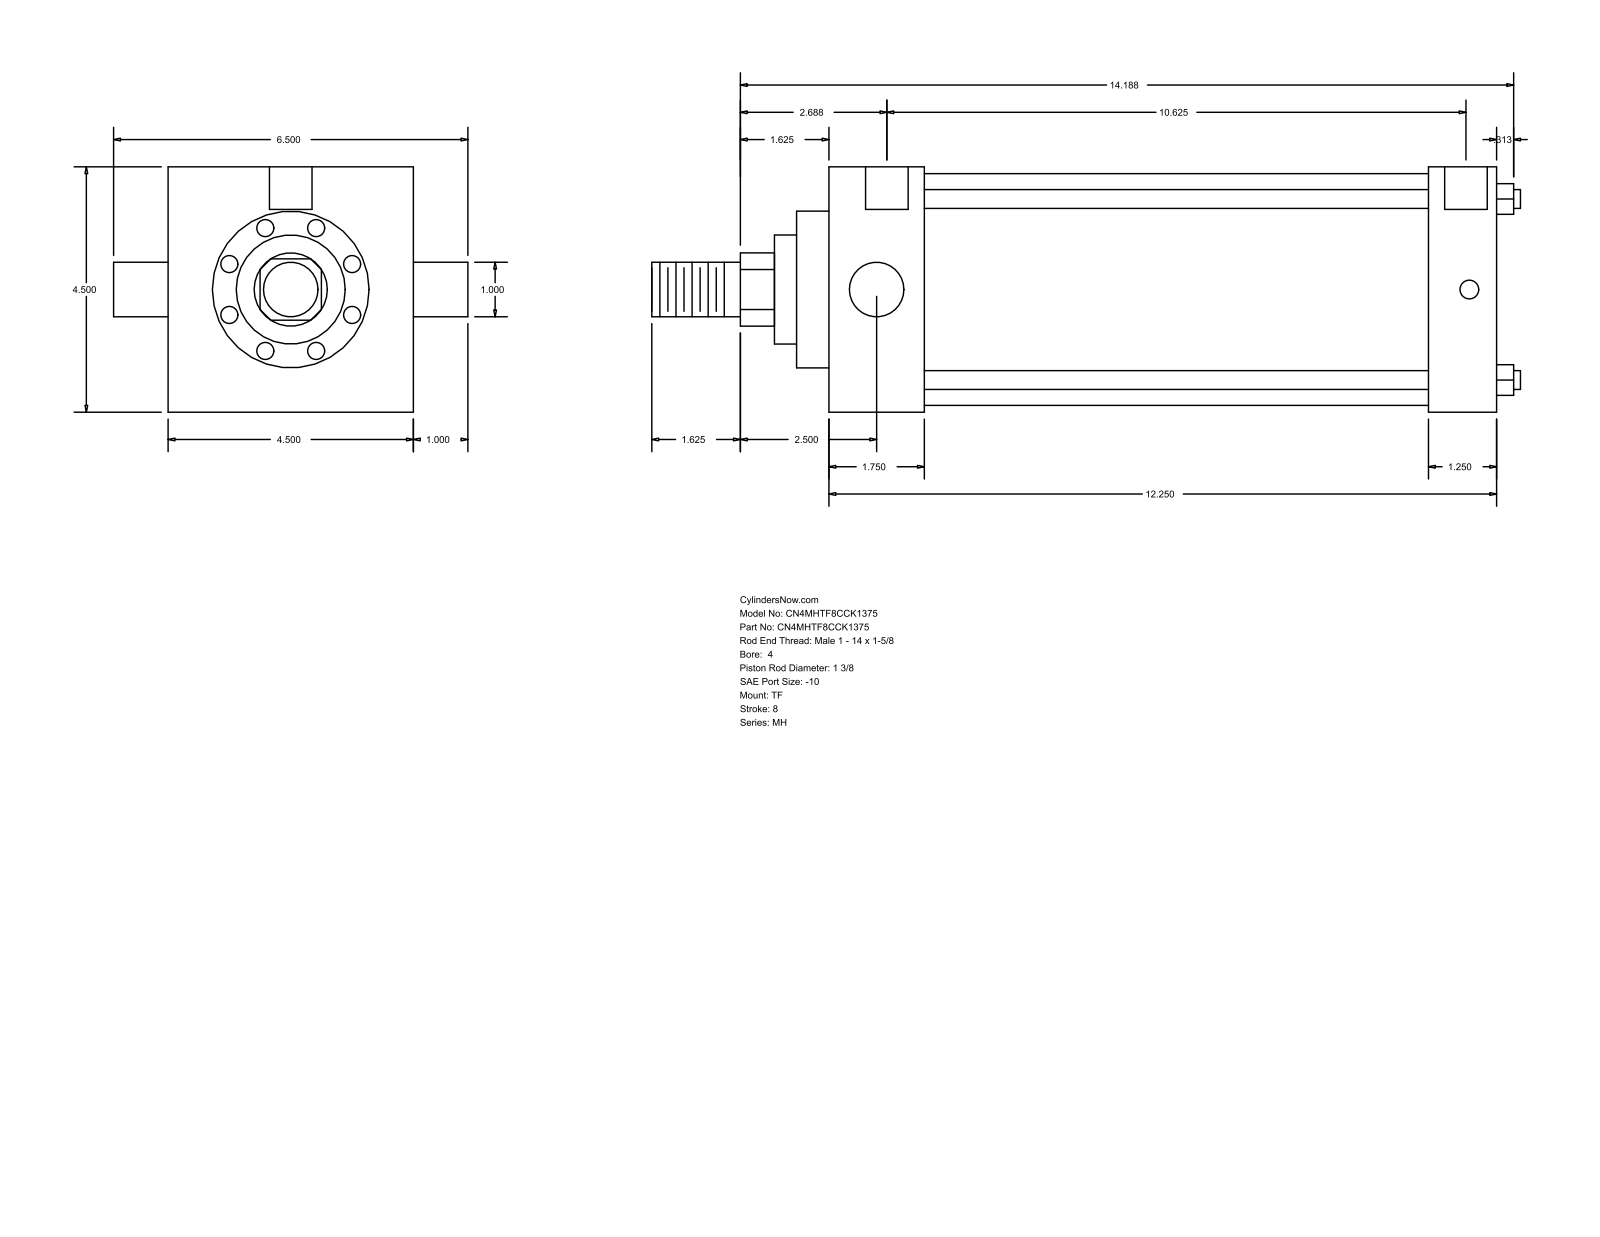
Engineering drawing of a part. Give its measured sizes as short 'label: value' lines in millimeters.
name: MH_TF__0400_1.375
written by: GSSL Pune (CONFIG_CONTROL_DESIGN)
unit: mm
bodies: 0 solids, 86 faces (61 planar, 25 cylindrical, 0 other)
size: 404.81 × 165.1 × 114.3
holes: 3× ⌀8.73, 2× ⌀19.84
bosses: 4× ⌀8.76, 2× ⌀25.4, 1× ⌀107.95, 1× ⌀73.03, 1× ⌀50.8, 1× ⌀34.92
rounds: 1× R17.06
face distances: 114.3, 311.16, 44.45, 266.71, 279.41, 234.96, 31.75, 15.08, 59.53, 294.49
hole spacings: 1.59, 271.47, 269.88, 273.06
